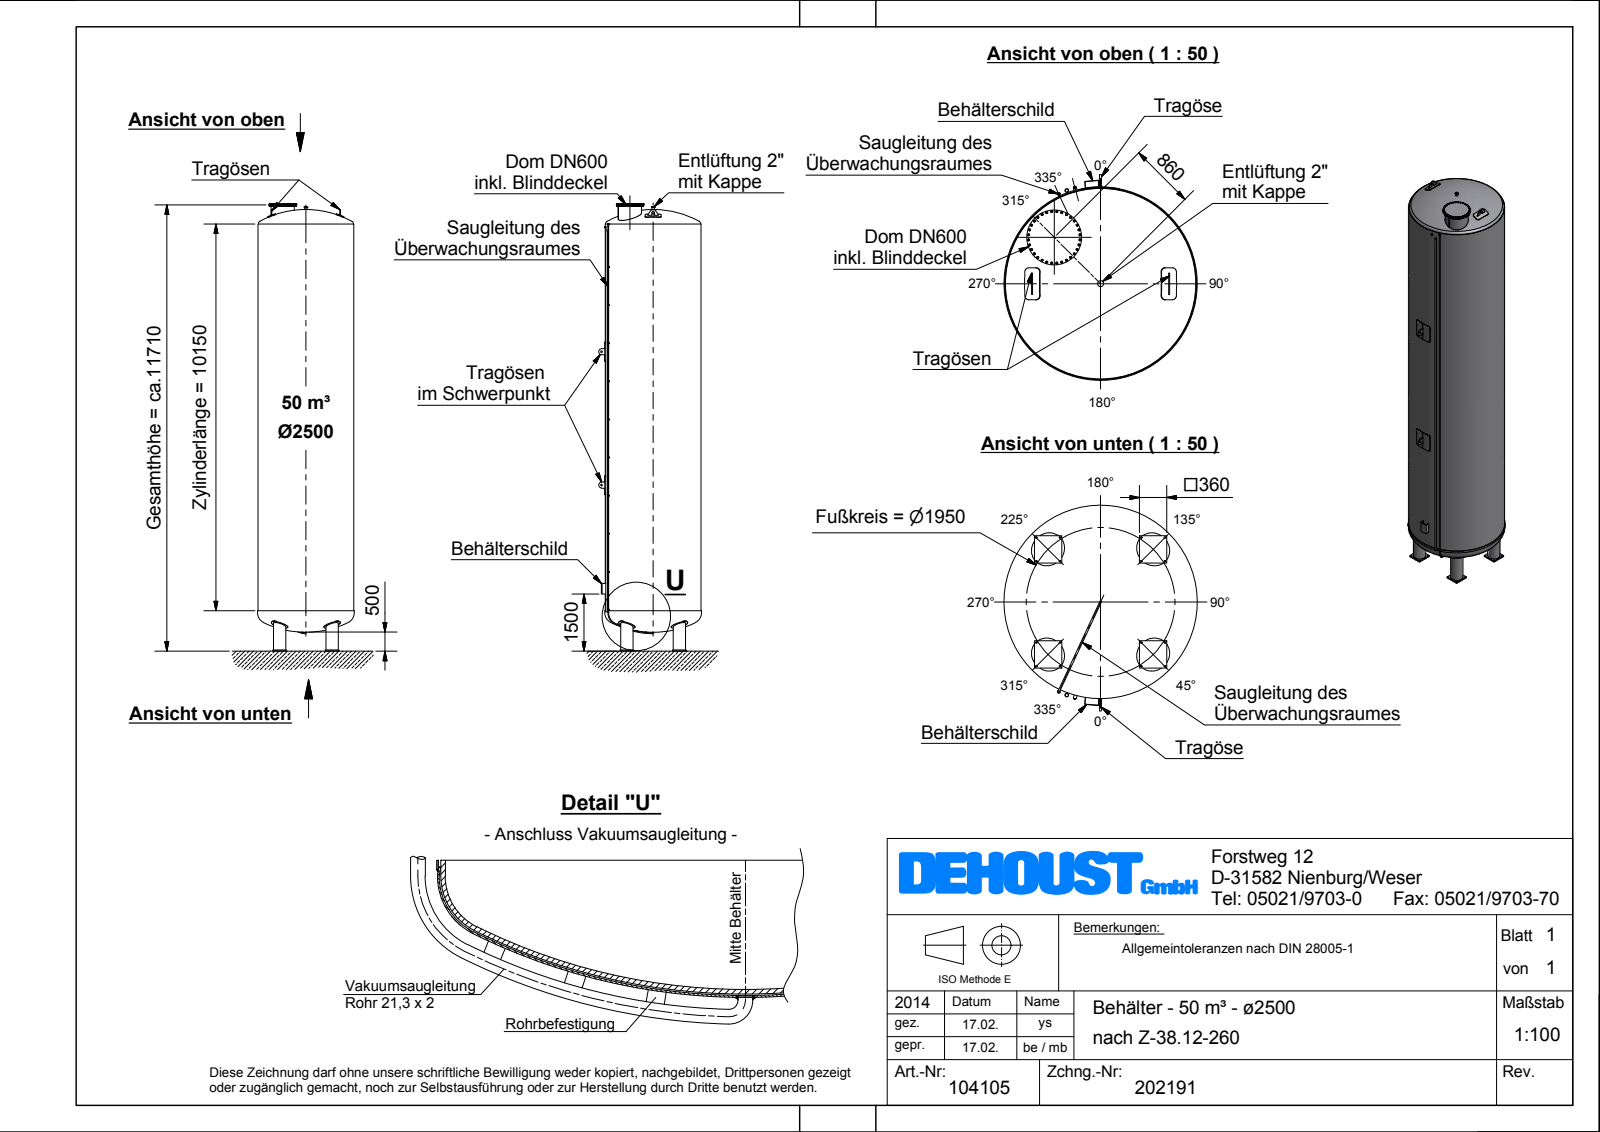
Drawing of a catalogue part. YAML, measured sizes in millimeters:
part_name: "Z-38_12-260_Beh\\S\\dlter_\\S\\x2500_050m\\S\\3_Dichte=1,0"
step_written_by: "Autodesk Inventor 2012 (AUTOMOTIVE_DESIGN)"
units: millimeters
bodies: {solids: 18, faces: 1249, planar: 751, cylindrical: 164, other: 334}
overall_size: [11738.78, 2700, 2540]
volume: 52560000000
surface_area: 115700000
round_holes:
  - {diameter: 200, count: 4}
  - {diameter: 306.9, count: 4}
  - {diameter: 598, count: 1}
round_bosses_or_shafts:
  - {diameter: 22.5, count: 32}
  - {diameter: 16, count: 32}
  - {diameter: 450, count: 4}
  - {diameter: 323.9, count: 4}
  - {diameter: 21.3, count: 2}
  - {diameter: 2540, count: 1}
  - {diameter: 2516, count: 1}
  - {diameter: 720, count: 1}
partial_cylinders:
  - {radius: 50, count: 8}
  - {radius: 56, count: 8}
  - {radius: 80, count: 2}
  - {radius: 35, count: 1}
  - {radius: 85, count: 1}
  - {radius: 1259, count: 1}
  - {radius: 1269, count: 1}
face_to_face_distances: [11211.09, 30, 11181.09, 11728.78, 11698.78, 517.69, 11693.78, 11663.78, 482.69, 35]
hole_center_spacings: [1378.86, 1300.09, 1950, 115, 1835]
